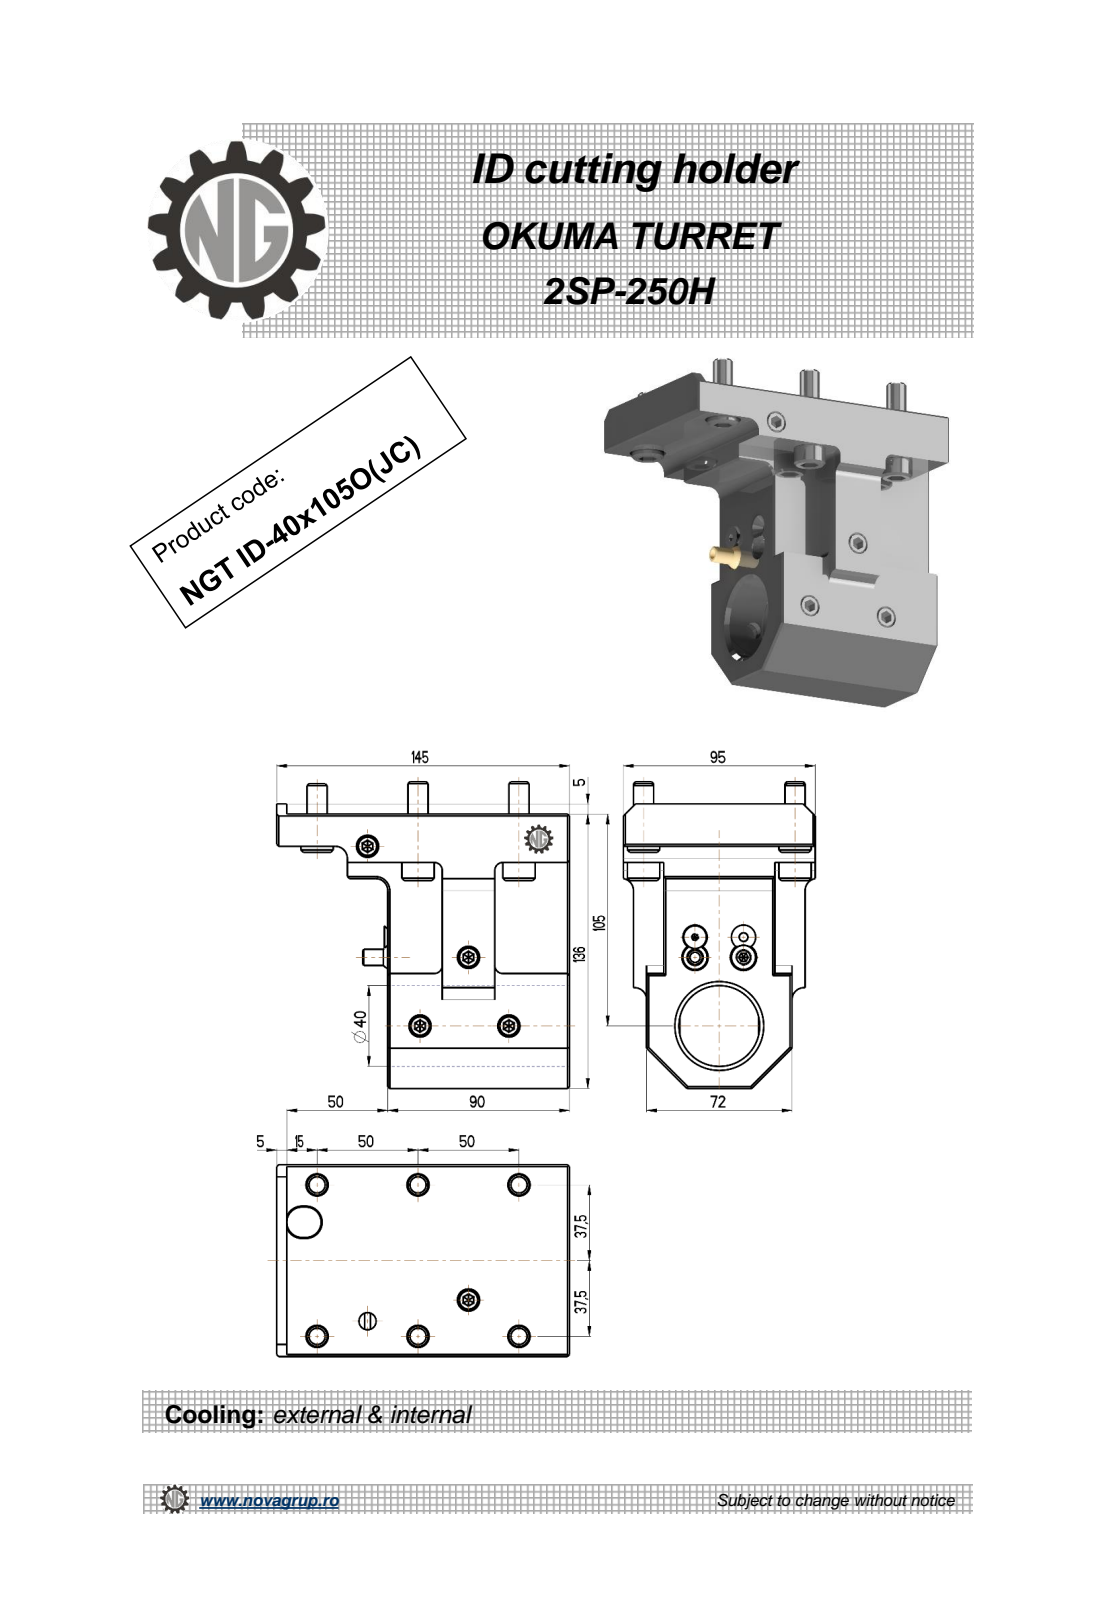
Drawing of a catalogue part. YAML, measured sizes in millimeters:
part_name: "NGT_ID_40_105O_JC"
step_written_by: "PRO/ENGINEER BY PARAMETRIC TECHNOLOGY CORPORATION, 2010280 (CONFIG_CONTROL_DESIGN)"
units: millimeters
bodies: {solids: 1, faces: 411, planar: 195, cylindrical: 121, other: 95}
overall_size: [152, 145, 95]
volume: 866032
surface_area: 92316
round_holes:
  - {diameter: 8.5, count: 3}
  - {diameter: 5, count: 1}
  - {diameter: 40, count: 1}
round_bosses_or_shafts:
  - {diameter: 16, count: 6}
  - {diameter: 10, count: 6}
  - {diameter: 11.2, count: 1}
  - {diameter: 8, count: 1}
partial_cylinders:
  - {radius: 0.32, count: 30}
  - {radius: 0.51, count: 24}
  - {radius: 0.22, count: 6}
  - {radius: 4, count: 4}
  - {radius: 6, count: 2}
  - {radius: 7.5, count: 2}
  - {radius: 0.4, count: 1}
face_to_face_distances: [20, 90, 75, 55, 11.5, 83.5, 8.5, 63.5, 5, 16]
hole_center_spacings: [36.06, 44]
